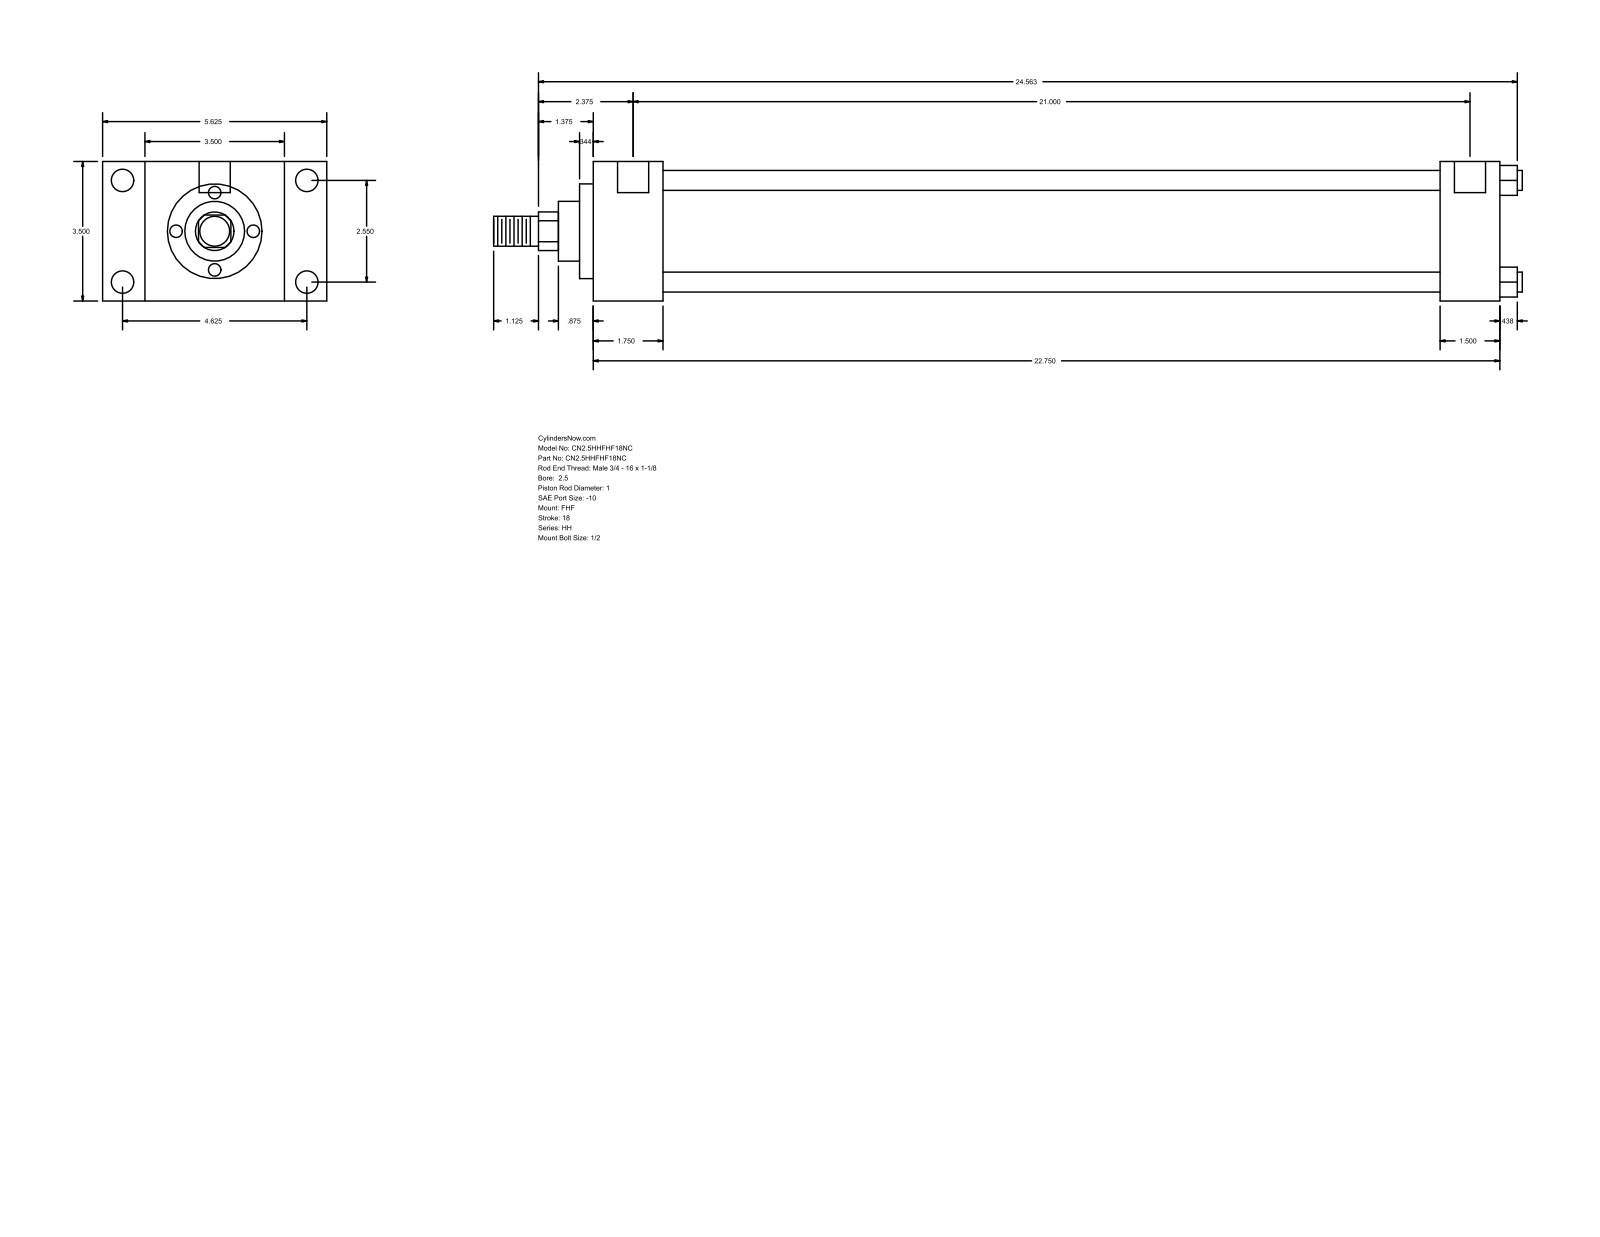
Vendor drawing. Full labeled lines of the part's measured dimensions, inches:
Part name (STEP PRODUCT): HH_FHF__0250_1
STEP written by: GSSL Pune (CONFIG_CONTROL_DESIGN)
Units: inches
Bodies: 0 solids, 90 faces (61 planar, 29 cylindrical, 0 other)
Overall size (bounding box): 25.813 × 5.625 × 3.5
Round holes (diameter × count): ⌀0.219 ×4, ⌀0.563 ×4, ⌀0.781 ×2
Round bosses / shafts (diameter × count): ⌀0.5 ×4, ⌀2.875 ×1, ⌀2.375 ×1, ⌀1.5 ×1, ⌀1 ×1, ⌀0.75 ×1
Partial cylindrical surfaces — rounded edges, fillets, slot ends (radius × count): R0.484 ×1
Main face-to-face distances: 3.5, 1.75, 1.063, 4.563, 22.75, 21, 5.625, 1.5, 21.25, 19.5
Hole centre spacings: 2.55, 4.625, 5.281, 21.125, 0.062, 0.063, 21, 21.062
